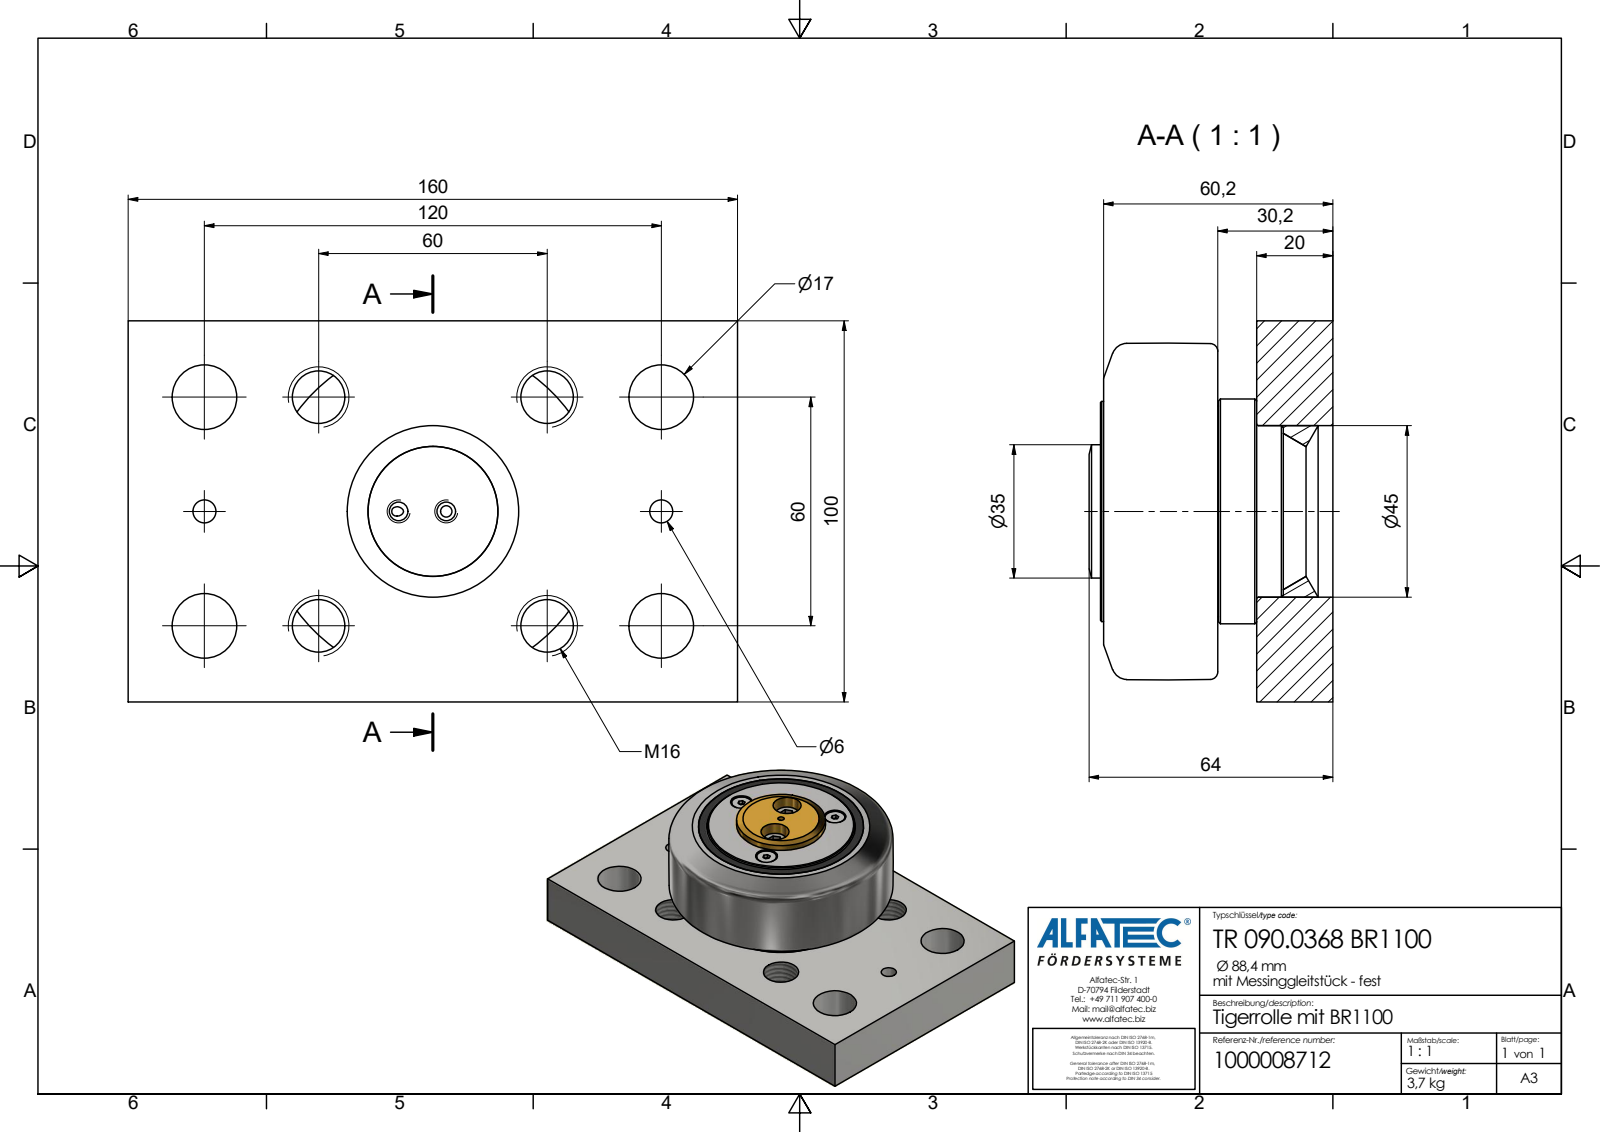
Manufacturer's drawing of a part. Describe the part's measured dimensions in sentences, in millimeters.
The part is named "TR 090.0368 BR1100_Kontur". Its 3-D file was written by "Autodesk Inventor 2020 (AP242_MANAGED_MODEL_BASED_3D_ENGINEERING_MIM_LF)". It is 1 solid with 86 faces: 44 planar, 28 cylindrical and 14 other. Overall it measures 160 by 100 by 64 millimeters. Its volume is 489 005 cubic millimeters and its surface area 66 315 square millimeters. Round holes: 4 of diameter 13.84, 4 of diameter 17, 3 of diameter 8.6, 2 of diameter 2.5, 2 of diameter 4.92, 2 of diameter 6, 2 of diameter 11, 1 of diameter 3, 1 of diameter 45. Round bosses or shafts: 3 of diameter 7.8, 1 of diameter 59, 1 of diameter 57.8, 1 of diameter 55.3, 1 of diameter 35. The main face-to-face distances are 20, 30.2, 100, 10.2, 160, 30, 60.2, 40.2, 61, 41. The hole center spacings are 30, 42.43, 60, 67.08, 90, 94.87, 108.17, 123.69.
